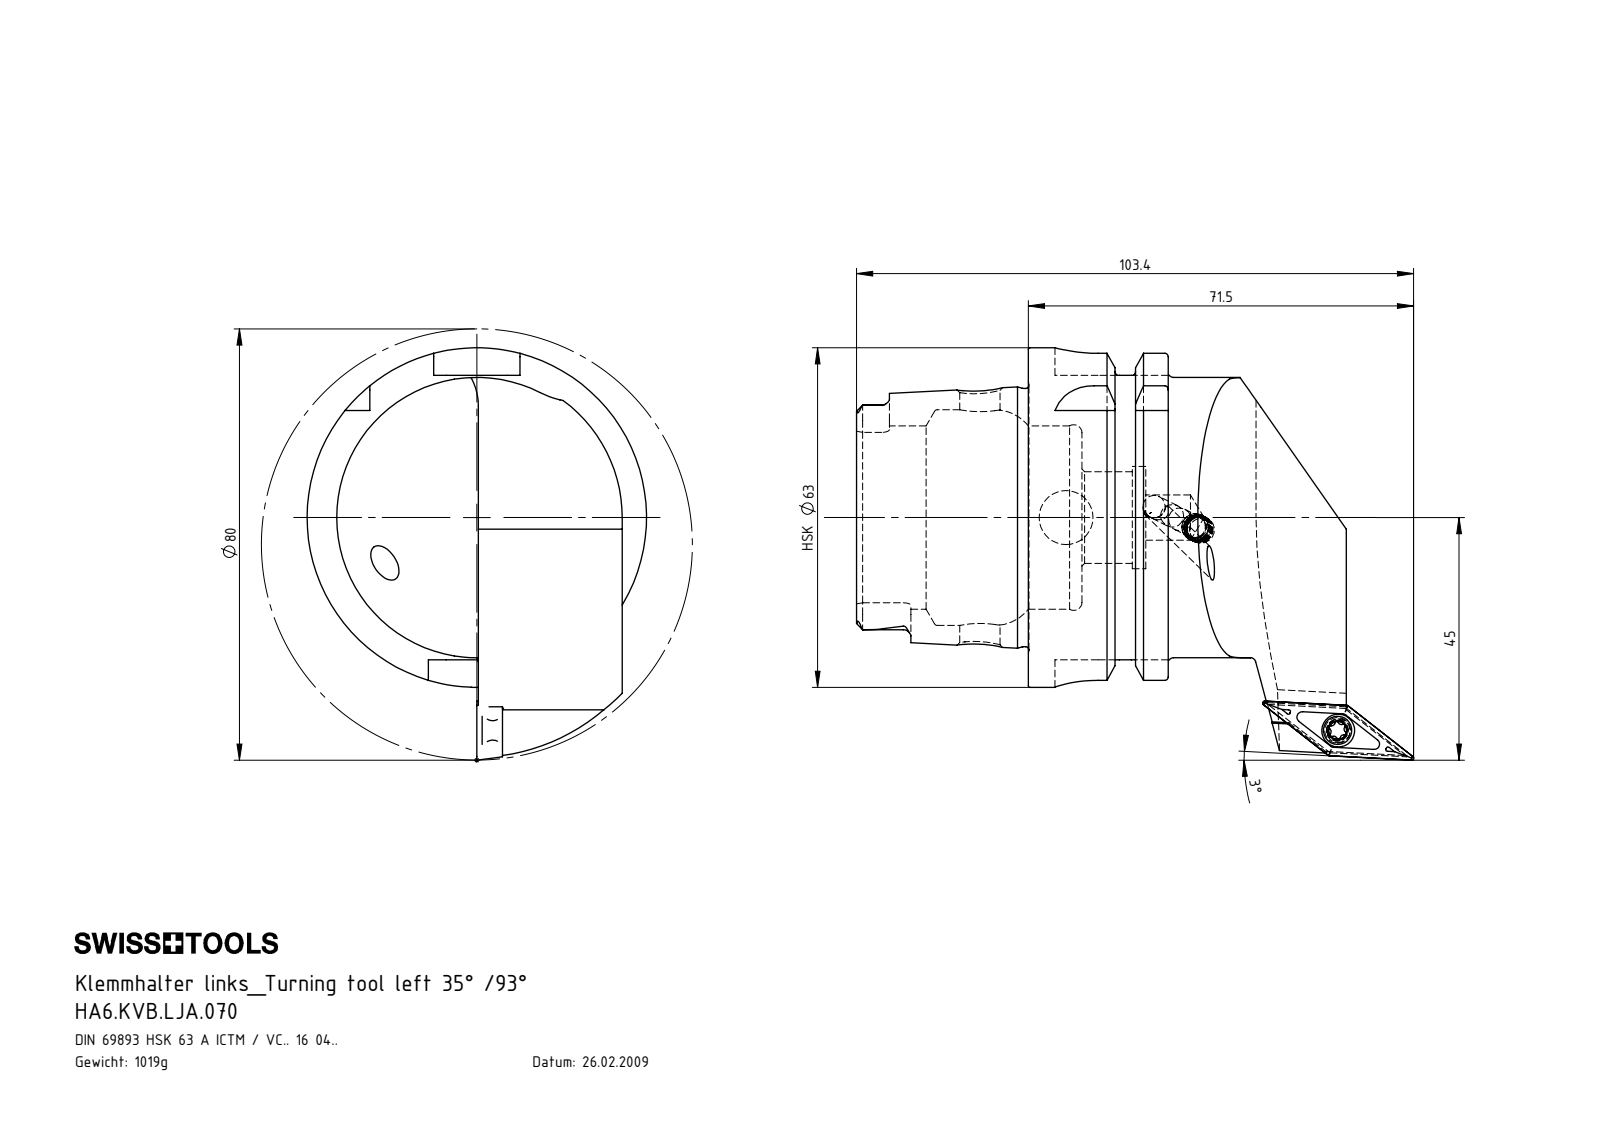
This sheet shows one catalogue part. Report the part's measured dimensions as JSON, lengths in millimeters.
{"part_name": "VCMT160404; HA6-KVB.LJA.070_A; WCB-ER2.001.009_A; KVT_MB_600_050 (+1 more)", "step_written_by": "SolidWorks 2017 (AUTOMOTIVE_DESIGN)", "units": "millimeters", "bodies": {"solids": 5, "faces": 317, "planar": 82, "cylindrical": 90, "other": 145}, "overall_size": [103.4, 76.5, 63], "volume_mm3": 126848, "surface_area_mm2": 29479, "round_holes": [[5, 2], [3.3, 1], [4, 1], [4.4, 1], [6, 1], [6.1, 1], [7.5, 1], [8.4, 1], [10, 1], [17, 1], [19, 1], [34, 1]], "round_bosses_or_shafts": [[63, 1], [54.95, 1], [52, 1], [47.94, 1], [5.25, 1], [5, 1], [4, 1]], "partial_cylinders_radius": [[0.34, 6], [0.59, 6], [1.4, 6], [8, 4], [2.82, 2], [2.88, 2], [6, 1], [11, 1]], "face_to_face_distances": [25.95, 16, 9.95, 26.2, 31.9, 41.85, 57.85, 52.8, 21.8, 11.85], "hole_center_spacings": [64.02, 64.13]}
